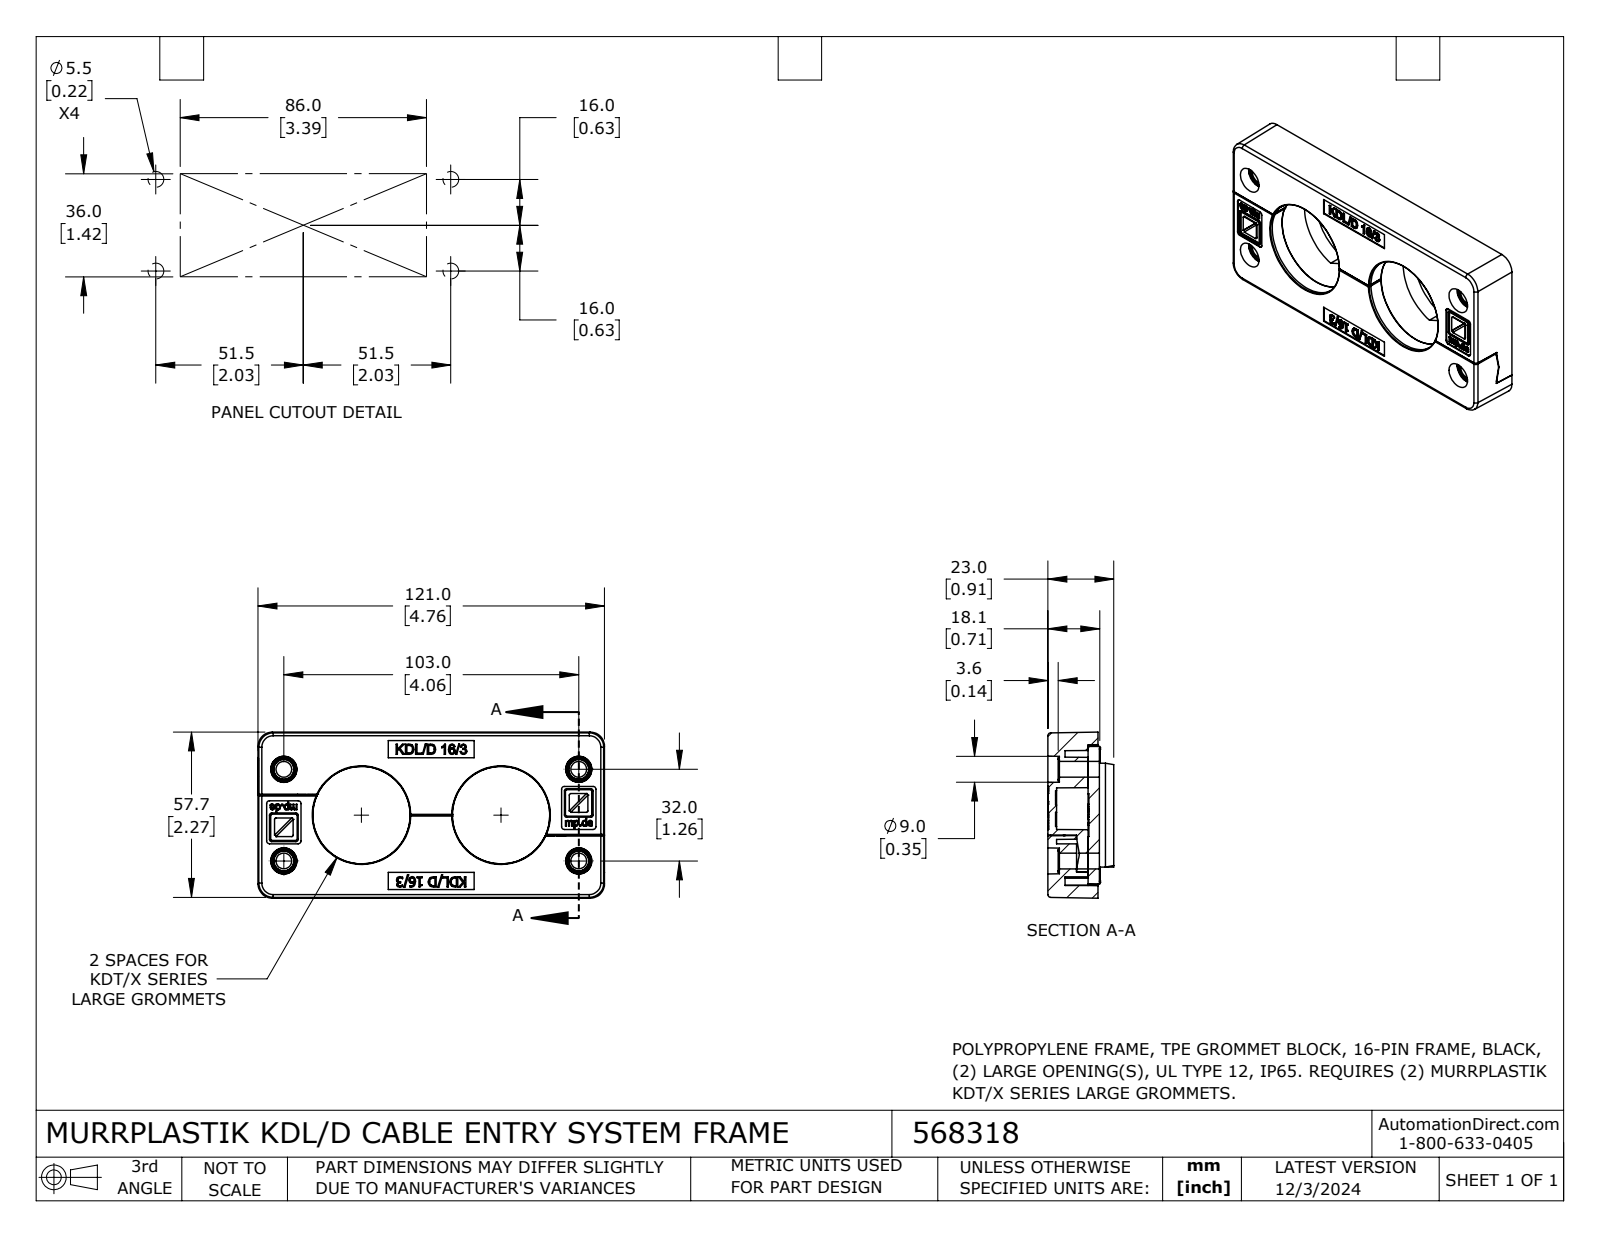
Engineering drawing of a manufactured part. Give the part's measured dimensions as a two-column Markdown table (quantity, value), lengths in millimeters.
| quantity | value |
| --- | --- |
| part name | 568318 |
| STEP written by | SolidWorks 2023 (CONFIG_CONTROL_DESIGN) |
| units | millimeters |
| bodies | 3 solids, 1209 faces (576 planar, 186 cylindrical, 447 other) |
| overall size | 121 × 58 × 23 |
| volume | 82 440 mm³ |
| surface area | 43 880 mm² |
| round holes (diameter × count) | 5 × 4, 5.5 × 4, 6 × 2, 35 × 2 |
| partial cylindrical surfaces (radius × count) | 0.2 × 36, 0.5 × 24, 1 × 23, 0.4 × 12, 0.8 × 8, 0.1 × 4, 0.2 × 4, 0.3 × 4 |
| main face-to-face distances | 6, 18, 4, 12, 14, 0.5, 11.5, 3.5, 8, 17.5 |
| hole center spacings | 10, 22, 7.5, 12, 14.5, 17.5, 27.8, 31.5 |
